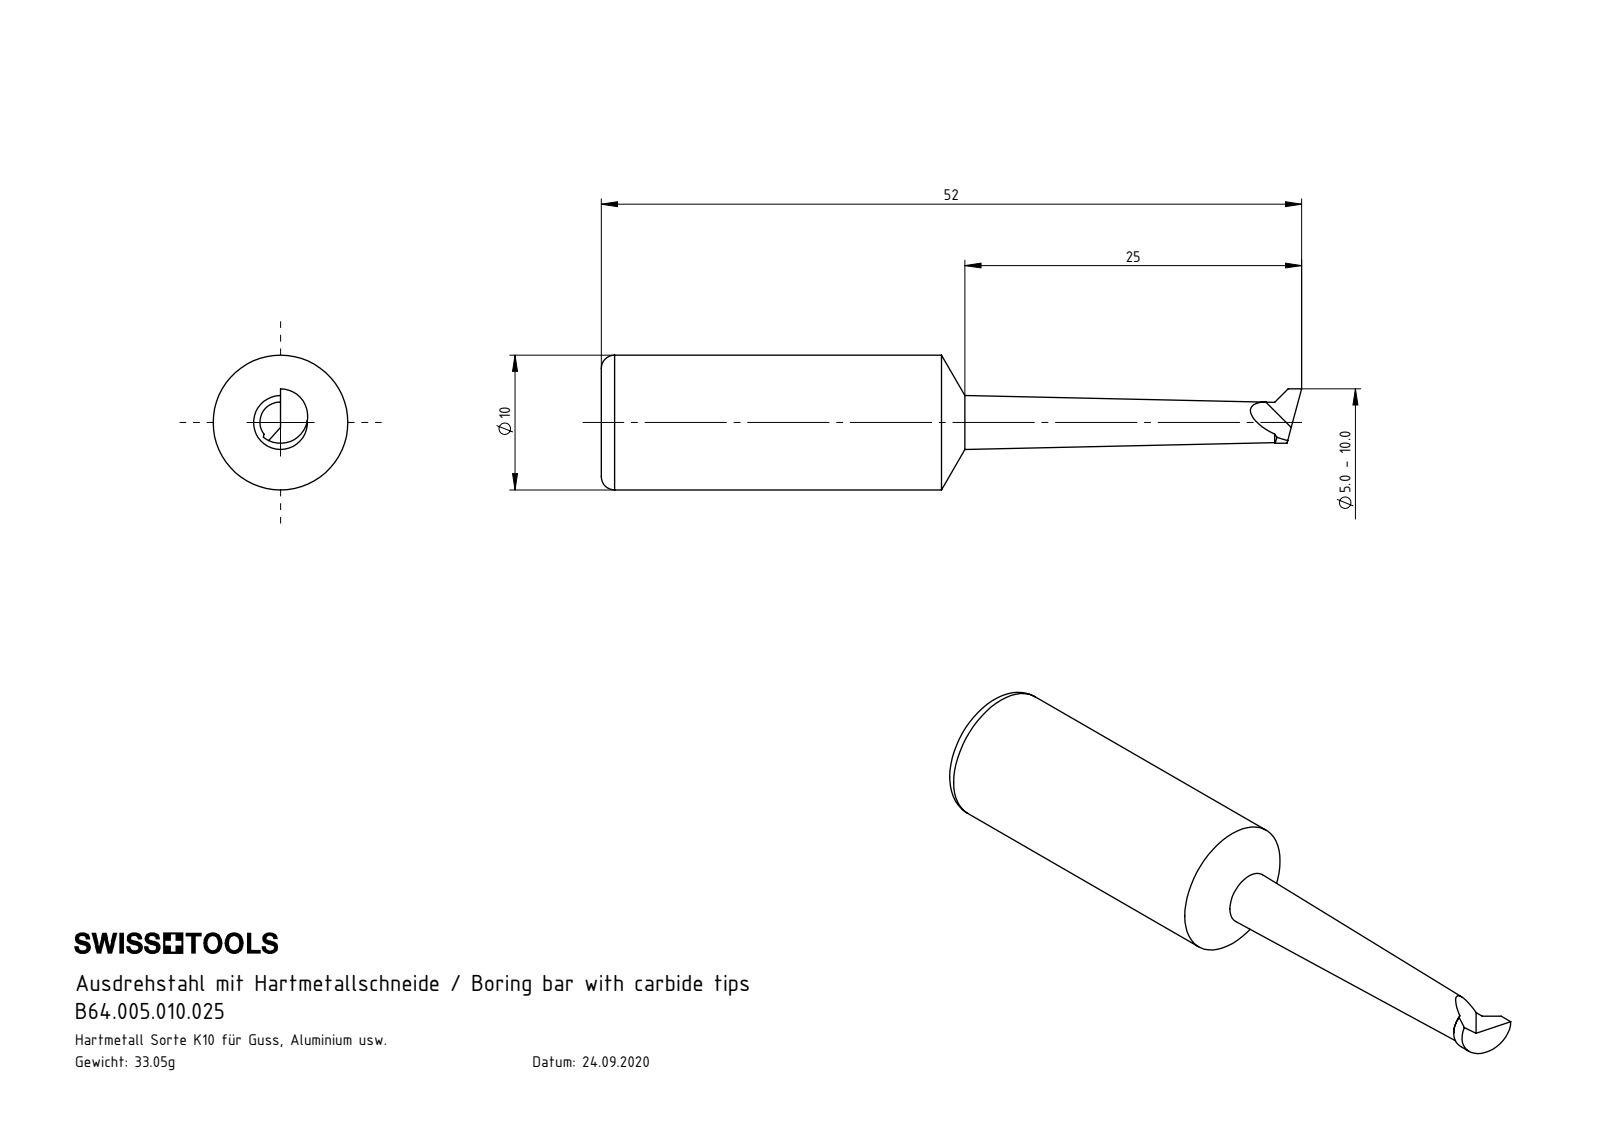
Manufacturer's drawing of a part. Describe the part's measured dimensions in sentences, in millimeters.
The part is named "B64.005.010.025". Its 3-D file was written by "SolidWorks 2022 (CONFIG_CONTROL_DESIGN)". It is 1 solid with 14 faces: 4 planar, 3 cylindrical and 7 other. Overall it measures 52 by 10 by 10 millimeters. Its volume is 2 280 cubic millimeters and its surface area 1 212 square millimeters. Round bosses or shafts: 1 of diameter 10. Partial cylindrical surfaces (rounded edges, fillets, slot ends): 1 of radius 2.02.
